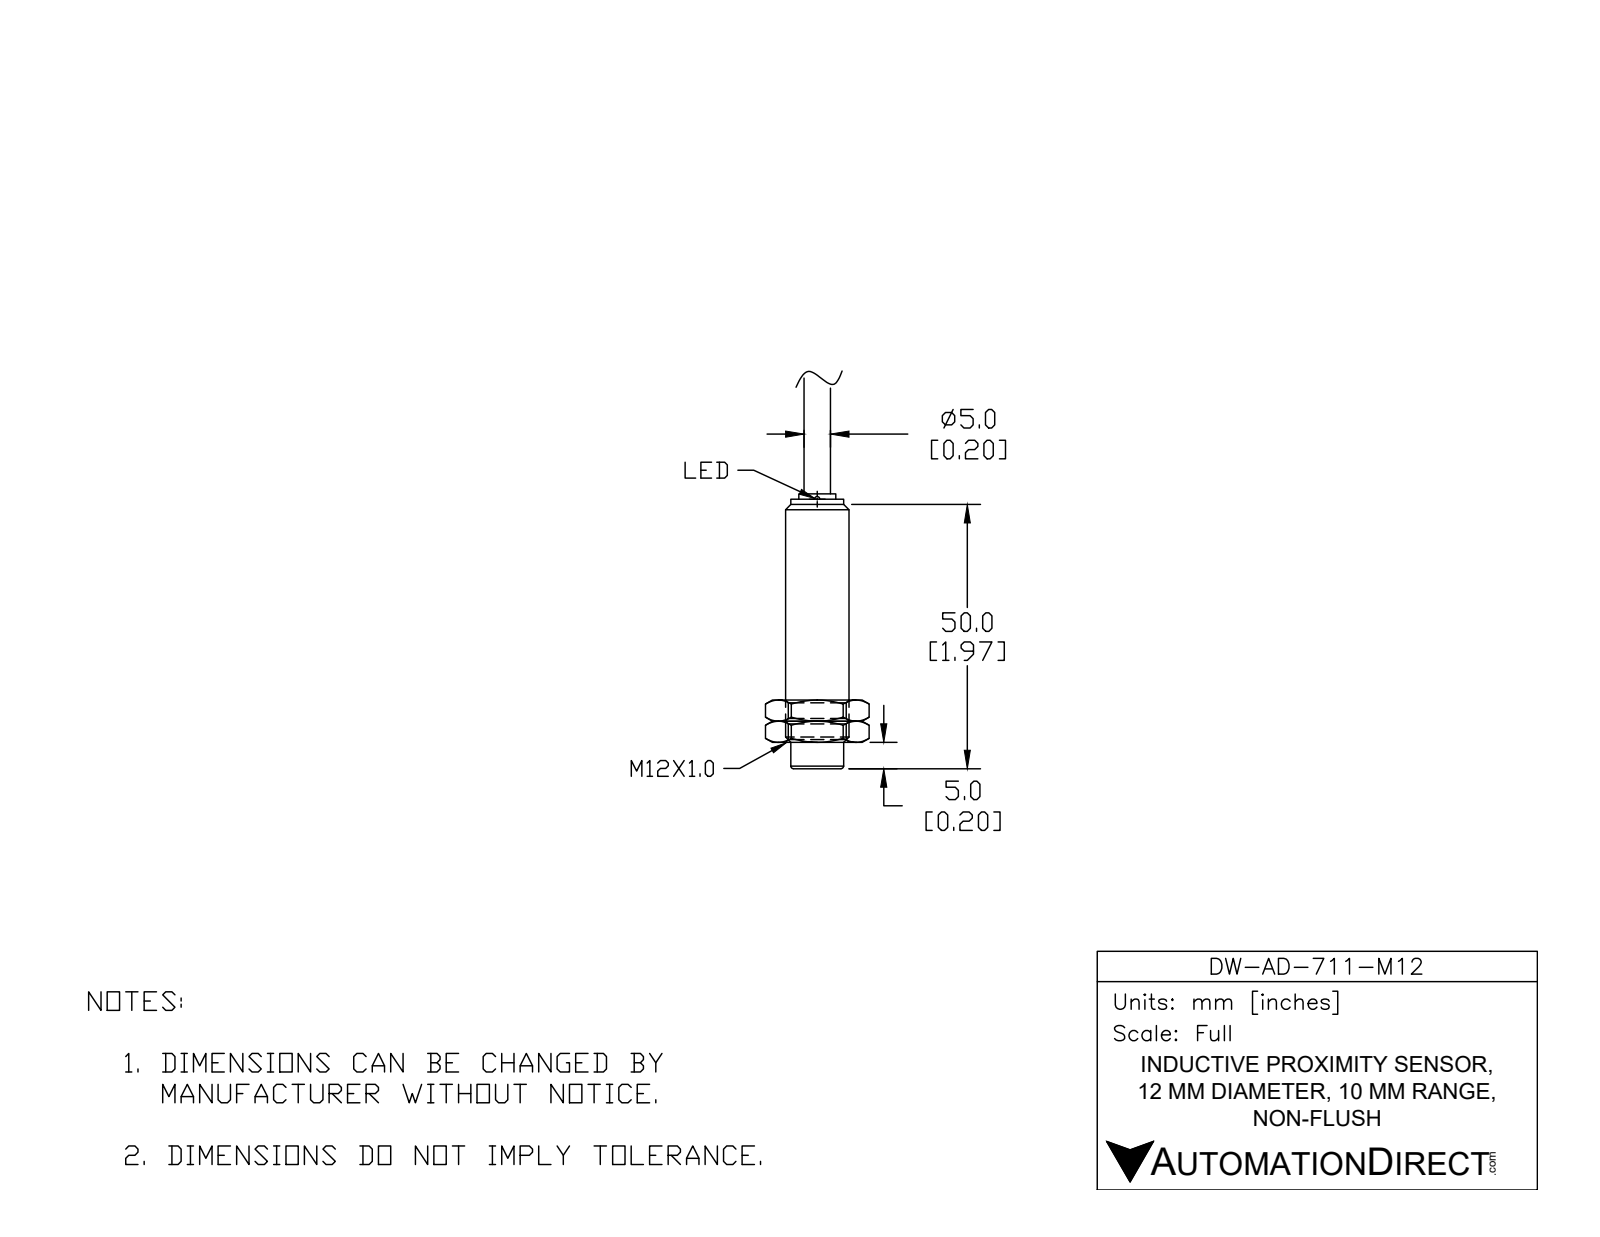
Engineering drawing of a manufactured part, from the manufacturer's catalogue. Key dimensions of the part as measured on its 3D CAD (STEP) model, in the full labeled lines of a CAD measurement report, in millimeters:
Part name (STEP PRODUCT): DW-AD-711-M12
STEP written by: SolidWorks 2017 (AUTOMOTIVE_DESIGN)
Units: millimetres
Bodies: 2 solids, 34 faces (17 planar, 6 cylindrical, 11 other)
Overall size (bounding box): 75.6 × 12 × 12
Volume: 6 180 mm³ · Surface area: 2 592 mm²
Round bosses / shafts (diameter × count): ⌀12 ×1, ⌀10.5 ×1, ⌀10.5 ×1, ⌀6.8 ×1, ⌀5 ×1, ⌀3 ×1
Main face-to-face distances: 52, 50.8, 1.2, 47, 3.8, 5, 51.6, 4.6, 0.8, 0.4
